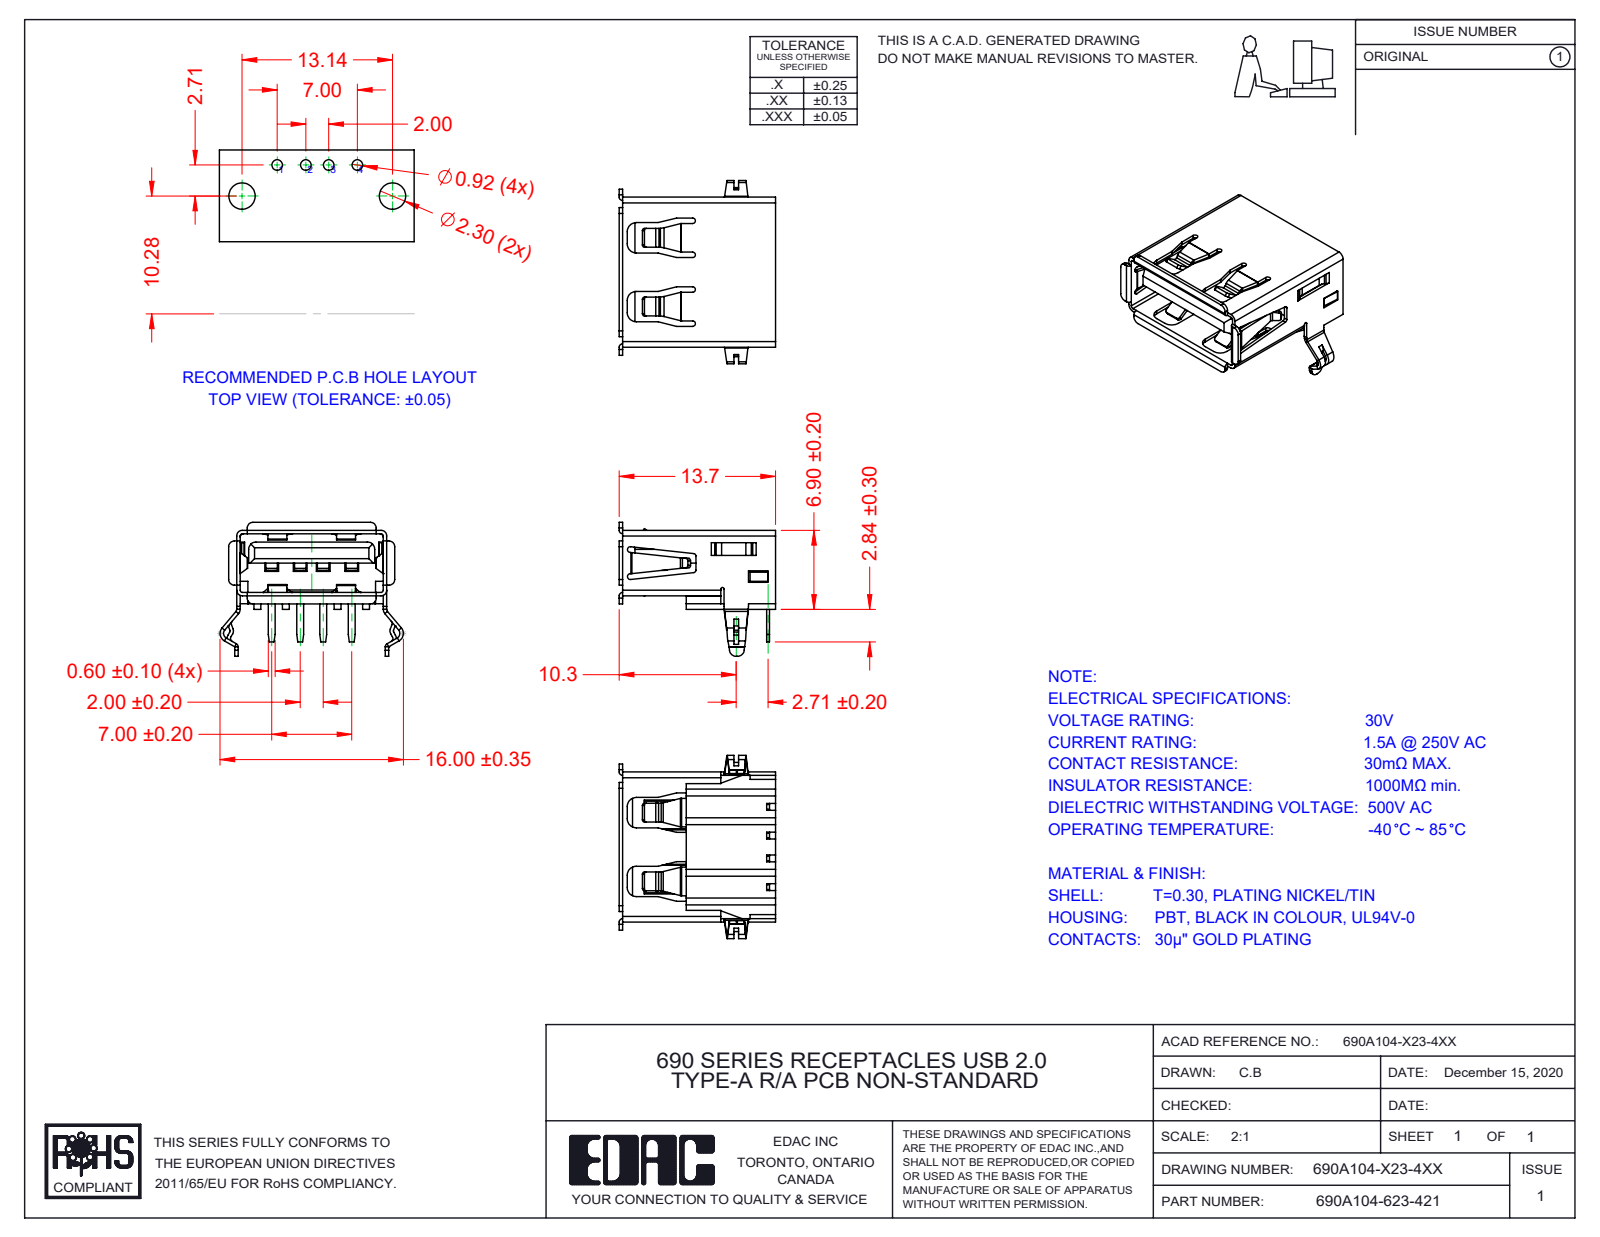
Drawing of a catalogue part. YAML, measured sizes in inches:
part_name: "690A104-123-411; Insulator 690A104-X23-4XX_Black; Shell 690A104-X23-4XX; Contact 690A104-X23-4XX"
step_written_by: "SolidWorks 2020 (AUTOMOTIVE_DESIGN)"
units: inches
bodies: {solids: 6, faces: 826, planar: 606, cylindrical: 184, other: 36}
overall_size: [0.63, 0.537, 0.461]
volume: 0.034
surface_area: 3.111
partial_cylinders:
  - {radius: 0.008, count: 30}
  - {radius: 0.02, count: 24}
  - {radius: 0.012, count: 12}
  - {radius: 0.004, count: 10}
  - {radius: 0.024, count: 8}
  - {radius: 0.031, count: 8}
  - {radius: 0.01, count: 6}
  - {radius: 0.009, count: 4}
face_to_face_distances: [0.213, 0.113, 0.101, 0.504, 0.05, 0.163, 0.04, 0.202, 0.225, 0.062]
